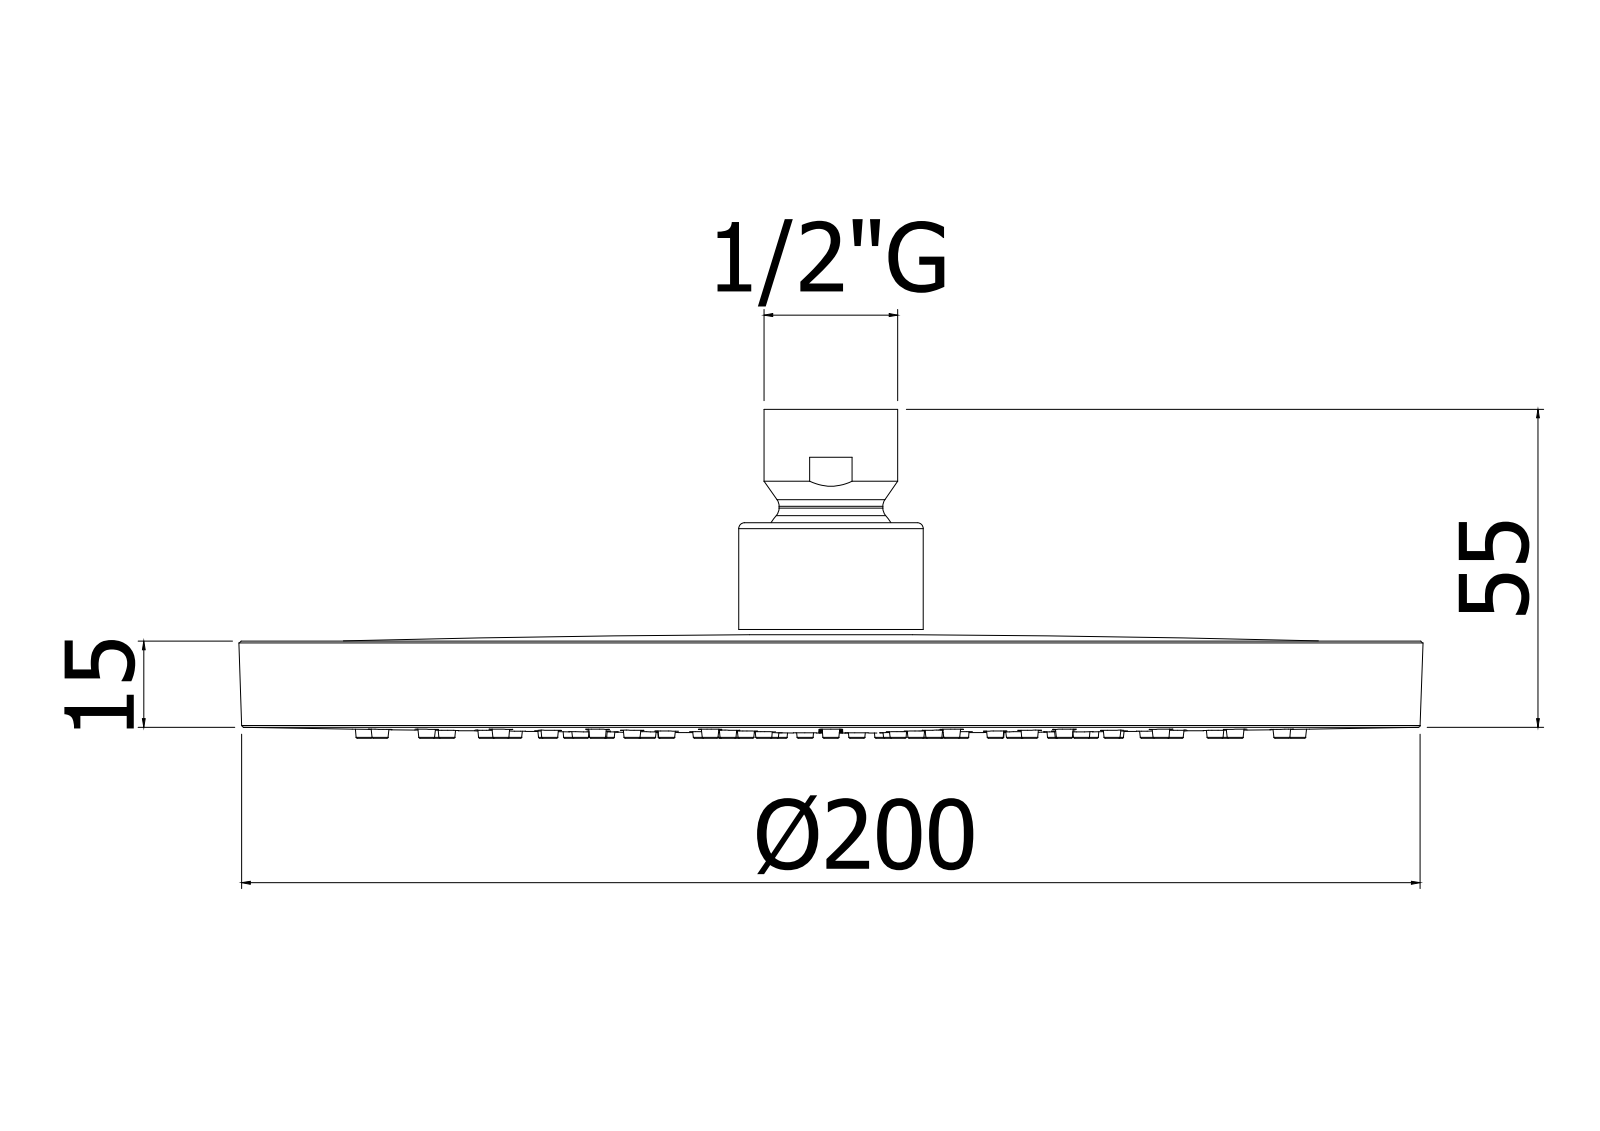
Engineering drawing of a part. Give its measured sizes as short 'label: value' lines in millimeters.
name: ZSOF115CR
written by: CREO PARAMETRIC BY PTC INC, 2020044 (CONFIG_CONTROL_DESIGN)
unit: mm
bodies: 2 solids, 3183 faces (398 planar, 325 cylindrical, 2460 other)
size: 205.49 × 205.49 × 58.38
volume: 241 709 mm³; area: 253 018 mm²
holes: 126× ⌀1, 1× ⌀7, 1× ⌀15, 1× ⌀24, 1× ⌀26.6, 1× ⌀28, 1× ⌀28.1
bosses: 1× ⌀195.62, 1× ⌀32, 1× ⌀23.2
rounds: 24× R0.5
face distances: 2, 9.86, 7.86, 9.68, 7.68, 3.14, 5.14, 12.82, 13, 20.54
hole spacings: 24, 21, 29.7, 40.57, 89.45, 48.94, 49.02, 56.15
